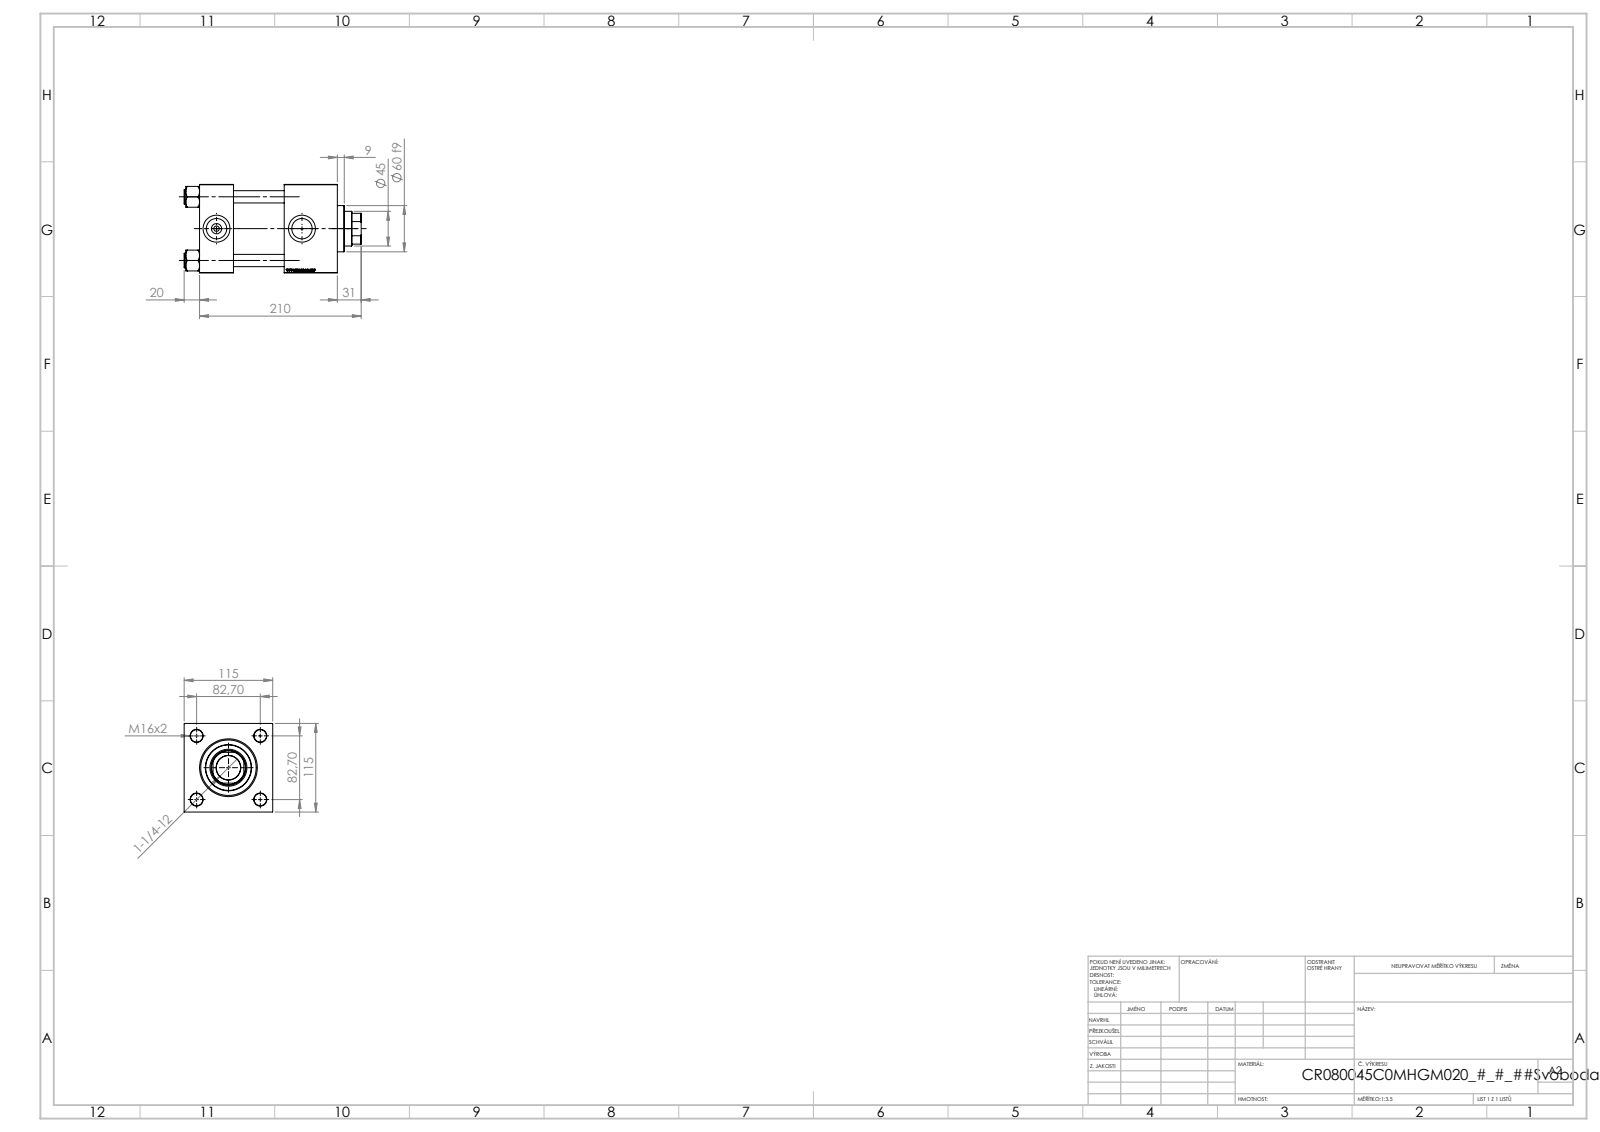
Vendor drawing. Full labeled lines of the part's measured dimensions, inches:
Part name (STEP PRODUCT): V215_VC_A; V215CR_VCP_C; V215CR_C_Body; NUT_M5_C (+1 more)
STEP written by: SolidWorks 2019 (CONFIG_CONTROL_DESIGN)
Units: inches
Bodies: 11 solids, 1196 faces (574 planar, 86 cylindrical, 536 other)
Overall size (bounding box): 9.055 × 4.528 × 4.528
Volume: 111 in³ · Surface area: 424.5 in²
Round holes (diameter × count): ⌀0.63 ×4, ⌀0.276 ×2, ⌀1.041 ×2, ⌀1.378 ×2, ⌀1.24 ×1, ⌀1.772 ×1, ⌀1.89 ×1, ⌀2.402 ×1, ⌀2.835 ×1, ⌀3.15 ×1
Round bosses / shafts (diameter × count): ⌀0.748 ×4, ⌀3.386 ×1, ⌀2.362 ×1
Partial cylindrical surfaces — rounded edges, fillets, slot ends (radius × count): R0.866 ×1
Main face-to-face distances: 4.528, 1.732, 4.331, 7.047, 5.315, 2.598, 2.717, 0.787, 5.917, 4.185
Hole centre spacings: 2.302, 3.256, 4.605, 4.37
